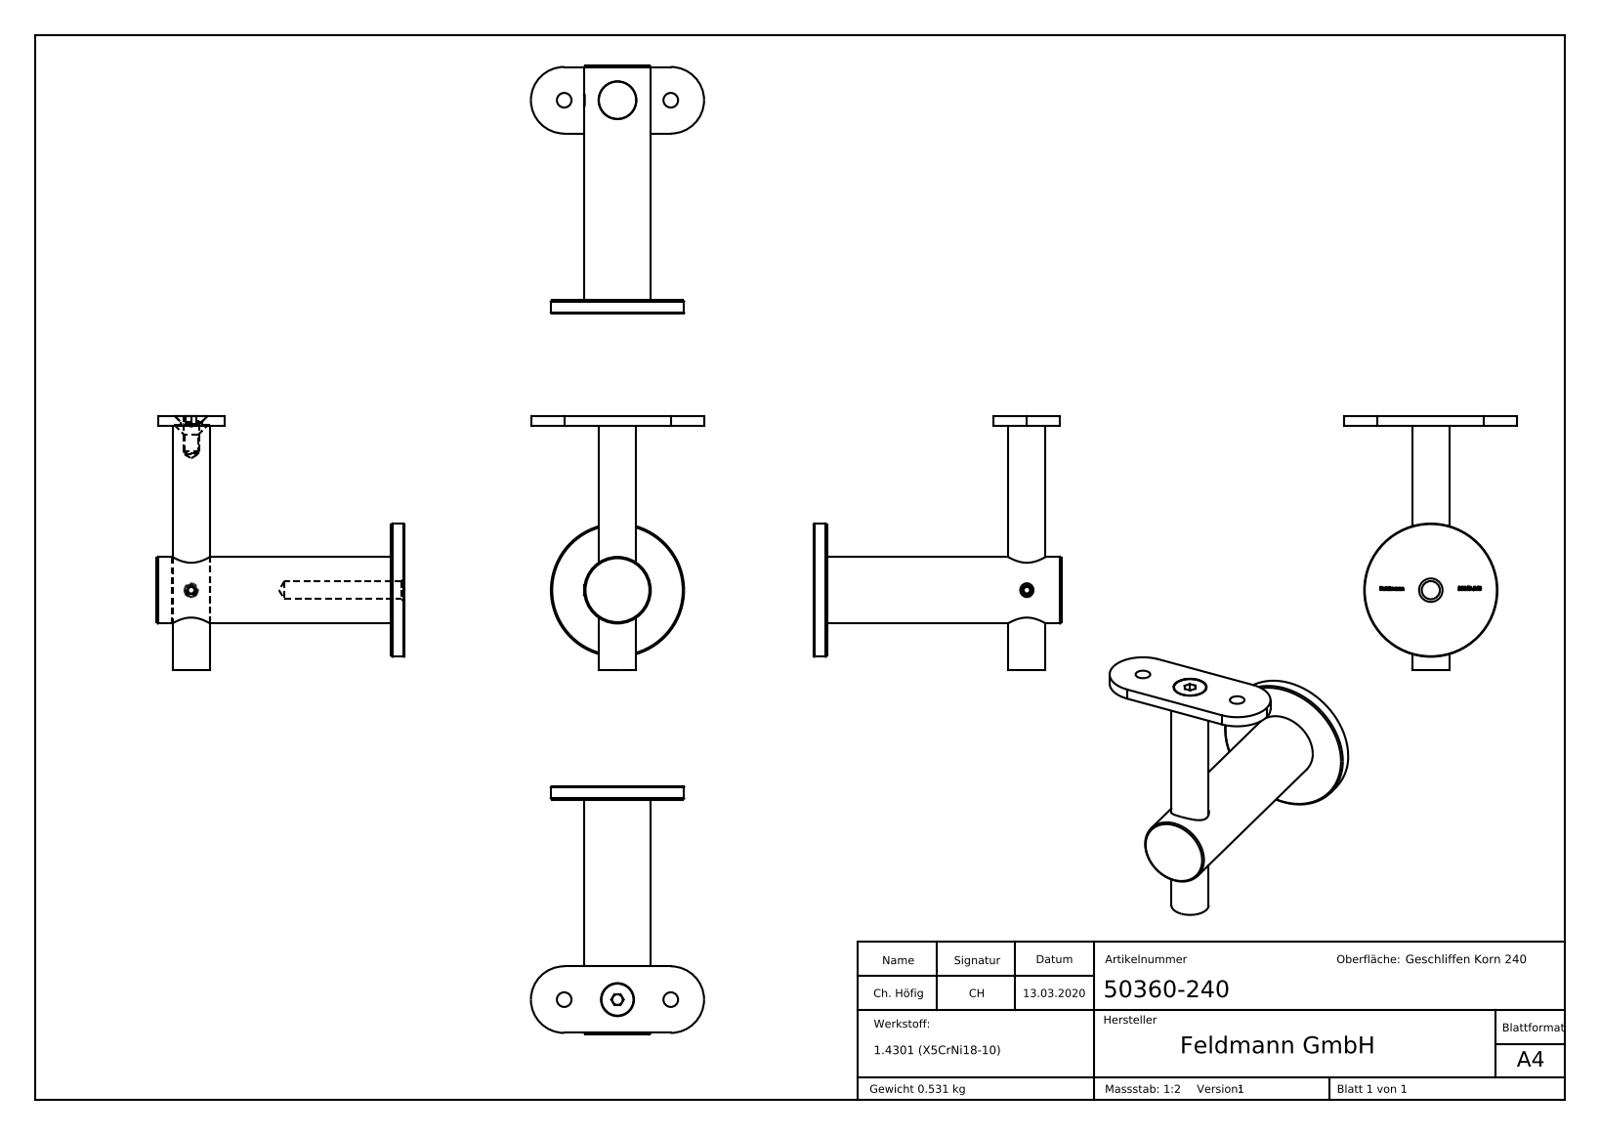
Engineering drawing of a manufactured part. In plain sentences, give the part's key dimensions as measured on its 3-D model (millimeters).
The part is named "503XX-240 Teil4; DIN-7991 M3-M10_DIN7991 M6x14; 50360-240; DIN913_DIN 913 M5x5 (+7 more)". Its 3-D file was written by "SolidWorks 2015 (CONFIG_CONTROL_DESIGN)". It is 5 solids with 298 faces: 152 planar, 19 cylindrical and 127 other. Overall it measures 95.5 by 93 by 88 millimeters. Its volume is 67 203 cubic millimeters and its surface area 22 027 square millimeters. Round holes: 2 of diameter 5.5, 1 of diameter 4.2, 1 of diameter 5, 1 of diameter 6.8, 1 of diameter 8.1, 1 of diameter 12.4, 1 of diameter 14.2. Round bosses or shafts: 1 of diameter 50, 1 of diameter 25, 1 of diameter 14, 1 of diameter 12, 1 of diameter 6, 1 of diameter 5. Partial cylindrical surfaces (rounded edges, fillets, slot ends): 2 of radius 12.5. The main face-to-face distances are 5, 4, 93, 88, 0.5, 92.5, 62.5, 67.5, 87.5, 25. The hole center spacings are 20, 40.
